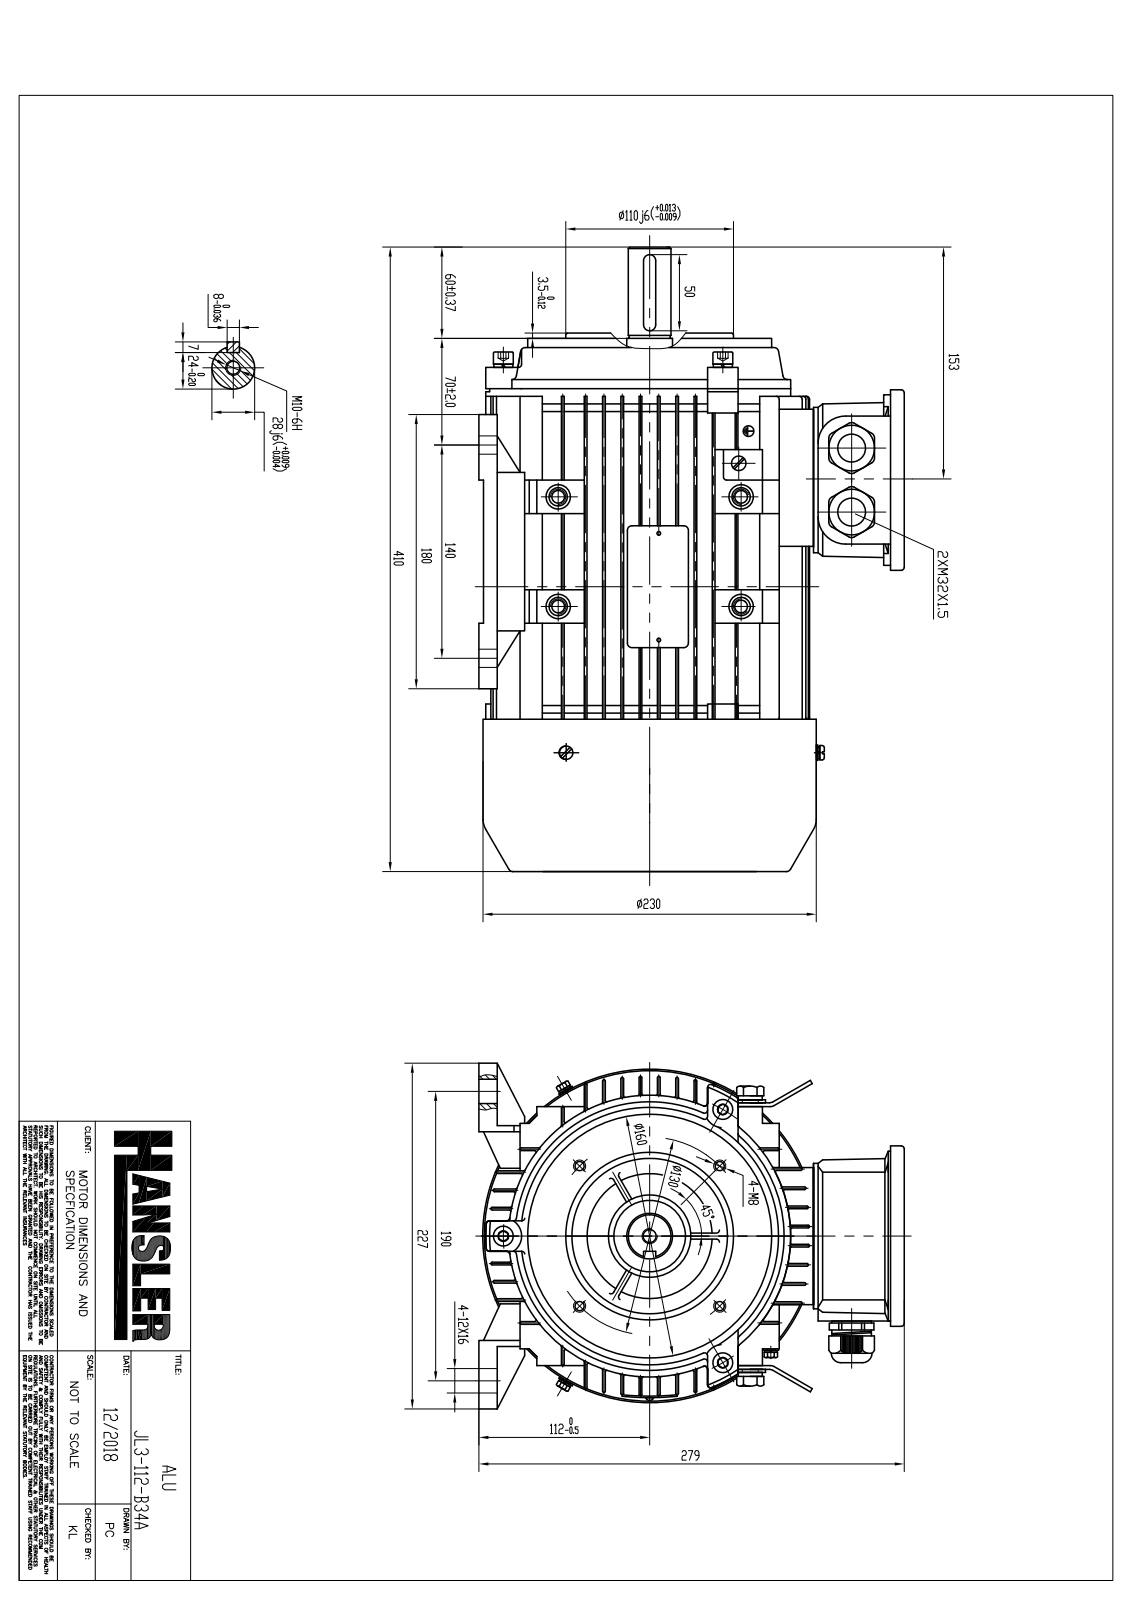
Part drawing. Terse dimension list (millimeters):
name: JL3-112-B34A
written by: SolidWorks 2018 (CONFIG_CONTROL_DESIGN)
unit: mm
bodies: 59 solids, 4589 faces (1981 planar, 1866 cylindrical, 742 other)
size: 395 × 288.66 × 239.33
volume: 2 744 000 mm³; area: 1 265 000 mm²
holes: 16× ⌀8, 10× ⌀5.8, 8× ⌀18, 6× ⌀5, 6× ⌀11, 4× ⌀4, 4× ⌀5.25, 4× ⌀5.3, 4× ⌀10, 4× ⌀10.55, 4× ⌀13, 3× ⌀3.85
bosses: 8× ⌀15, 8× ⌀12, 8× ⌀10, 8× ⌀5, 4× ⌀17, 4× ⌀16, 4× ⌀15.75, 4× ⌀9.5
rounds: 656× R0.5, 142× R1, 39× R3, 32× R2, 25× R5, 20× R4, 16× R0.3, 14× R6
face distances: 1.8, 15, 100, 14, 85, 16.8, 71, 115, 29, 56
hole spacings: 84.34, 98, 21.26, 43.86, 1.41, 18, 20.74, 21.21
